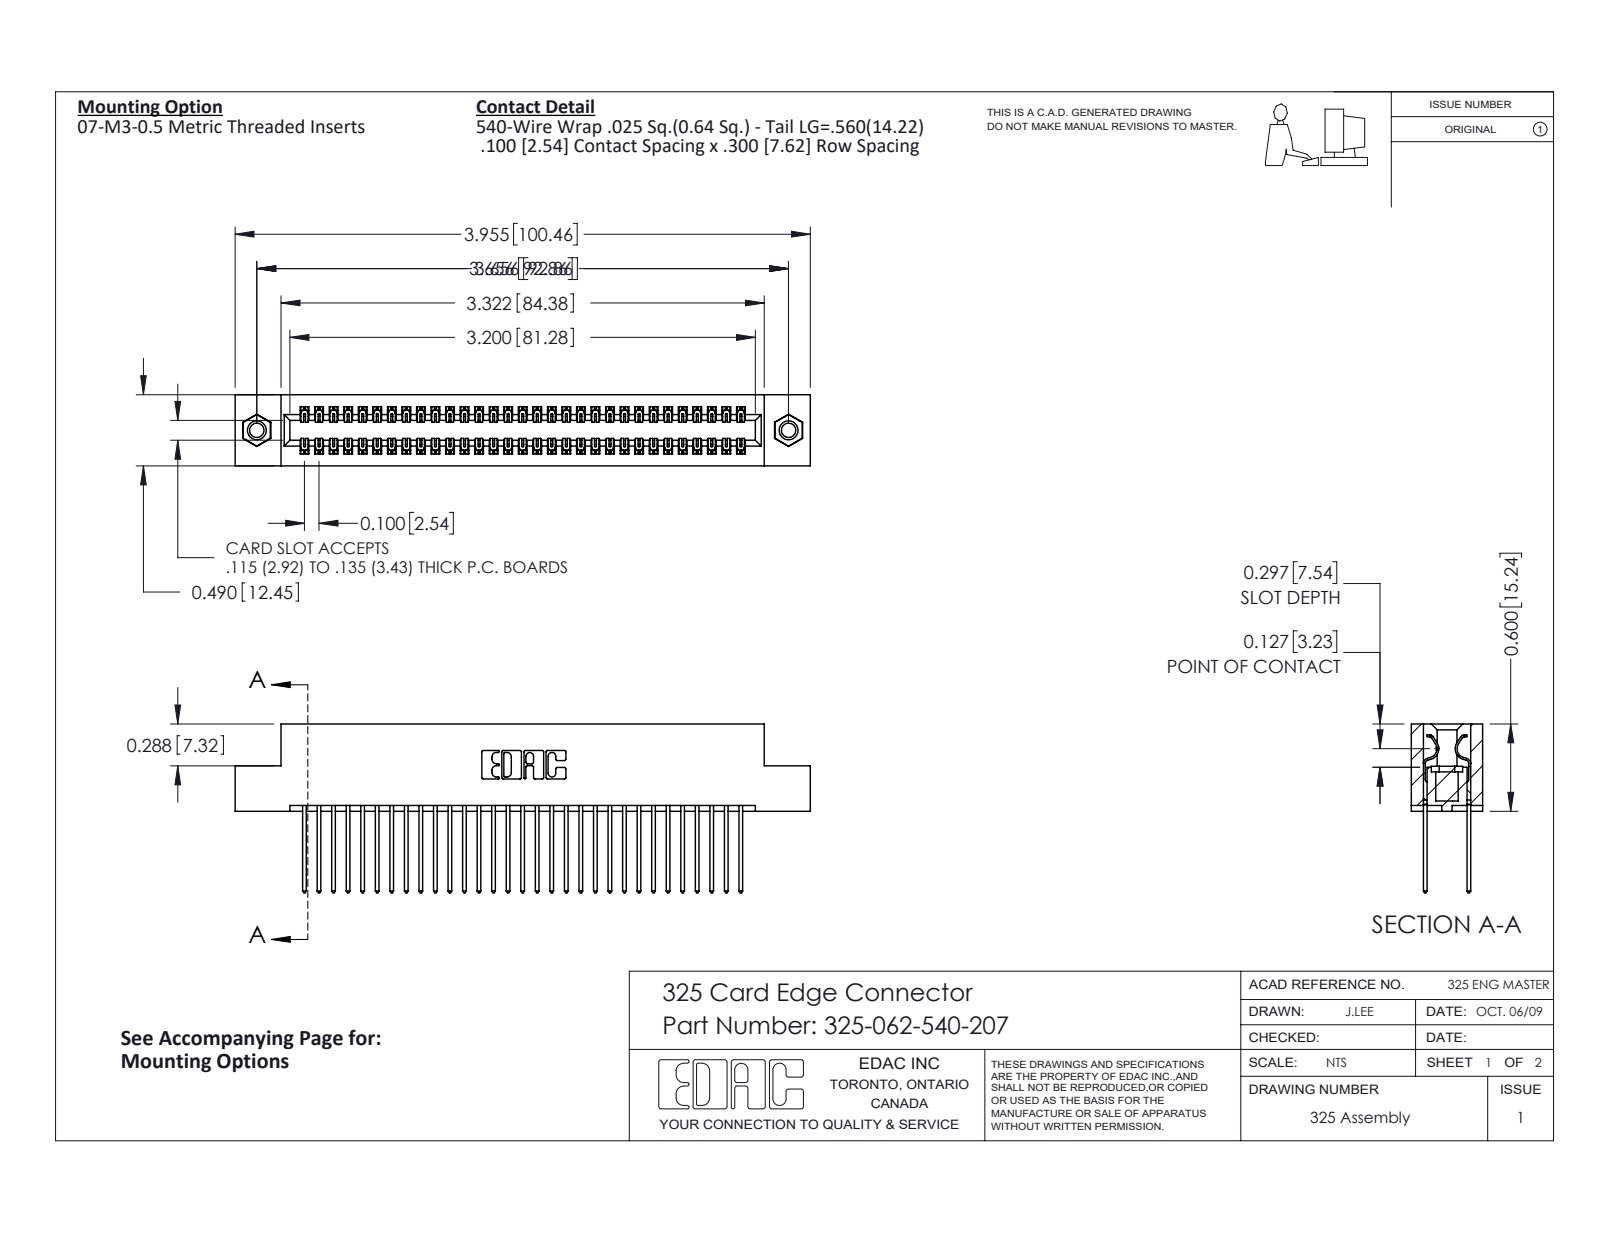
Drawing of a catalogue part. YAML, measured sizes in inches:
part_name: "325-062-540-207; 325 Part_TI; 345-250-001_345-250-005-103; 325-292-001_325-293-140"
step_written_by: "SolidWorks 2016 (CONFIG_CONTROL_DESIGN)"
units: inches
bodies: {solids: 65, faces: 3398, planar: 2334, cylindrical: 1048, other: 16}
overall_size: [3.955, 1.16, 0.49]
volume: 0.799
surface_area: 25.93
round_holes:
  - {diameter: 0.098, count: 2}
  - {diameter: 0.125, count: 2}
  - {diameter: 0.16, count: 2}
round_bosses_or_shafts:
  - {diameter: 0.155, count: 2}
partial_cylinders:
  - {radius: 0.006, count: 93}
  - {radius: 0.01, count: 62}
  - {radius: 0.01, count: 22}
  - {radius: 0.007, count: 6}
  - {radius: 0.031, count: 6}
  - {radius: 0.026, count: 3}
  - {radius: 0.014, count: 2}
  - {radius: 0.022, count: 2}
face_to_face_distances: [0.083, 0.407, 0.3, 0.107, 0.383, 0.025, 0.49, 0.325, 0.275, 0.04]
hole_center_spacings: [3.656]
